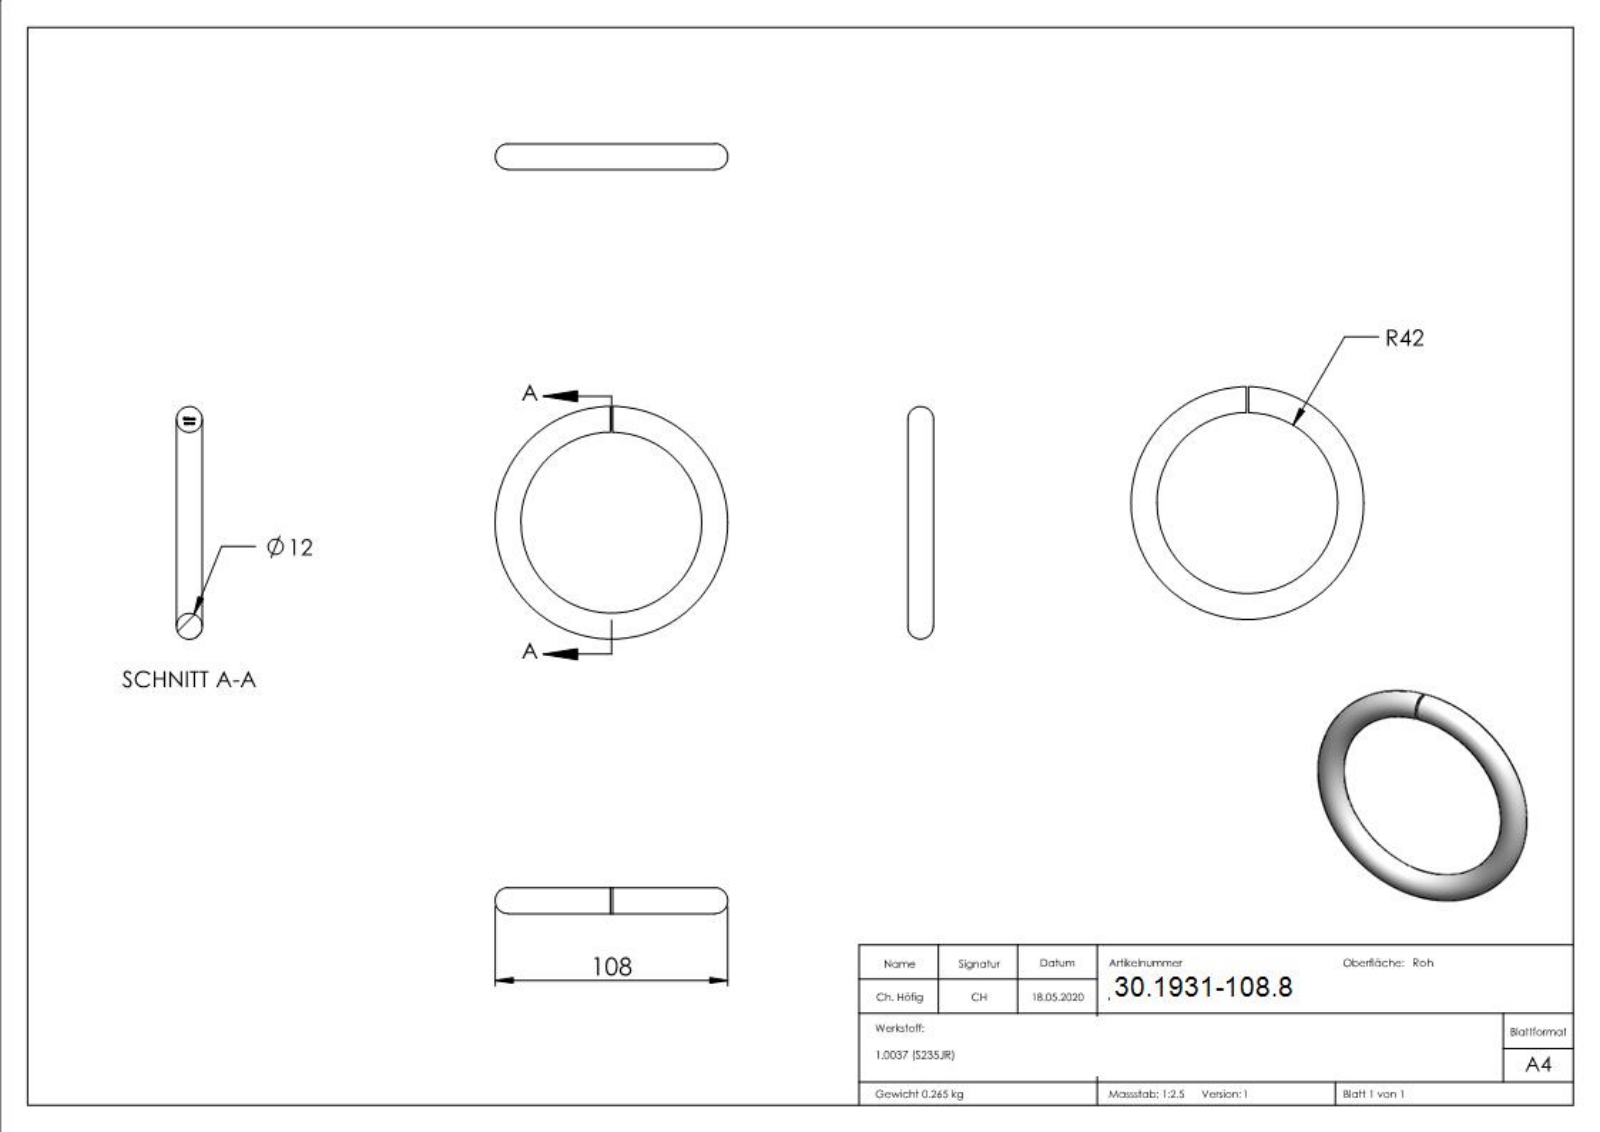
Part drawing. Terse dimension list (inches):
name: 5630-108
written by: SolidWorks 2015 (CONFIG_CONTROL_DESIGN)
unit: in
bodies: 1 solid, 211 faces (108 planar, 0 cylindrical, 103 other)
size: 4.252 × 4.252 × 0.472
volume: 2.074 in³; area: 17.96 in²
face distances: 0.039, 0.059, 0.02, 0.07, 0.033, 0.096, 0.083, 0.039, 0.024, 0.107
